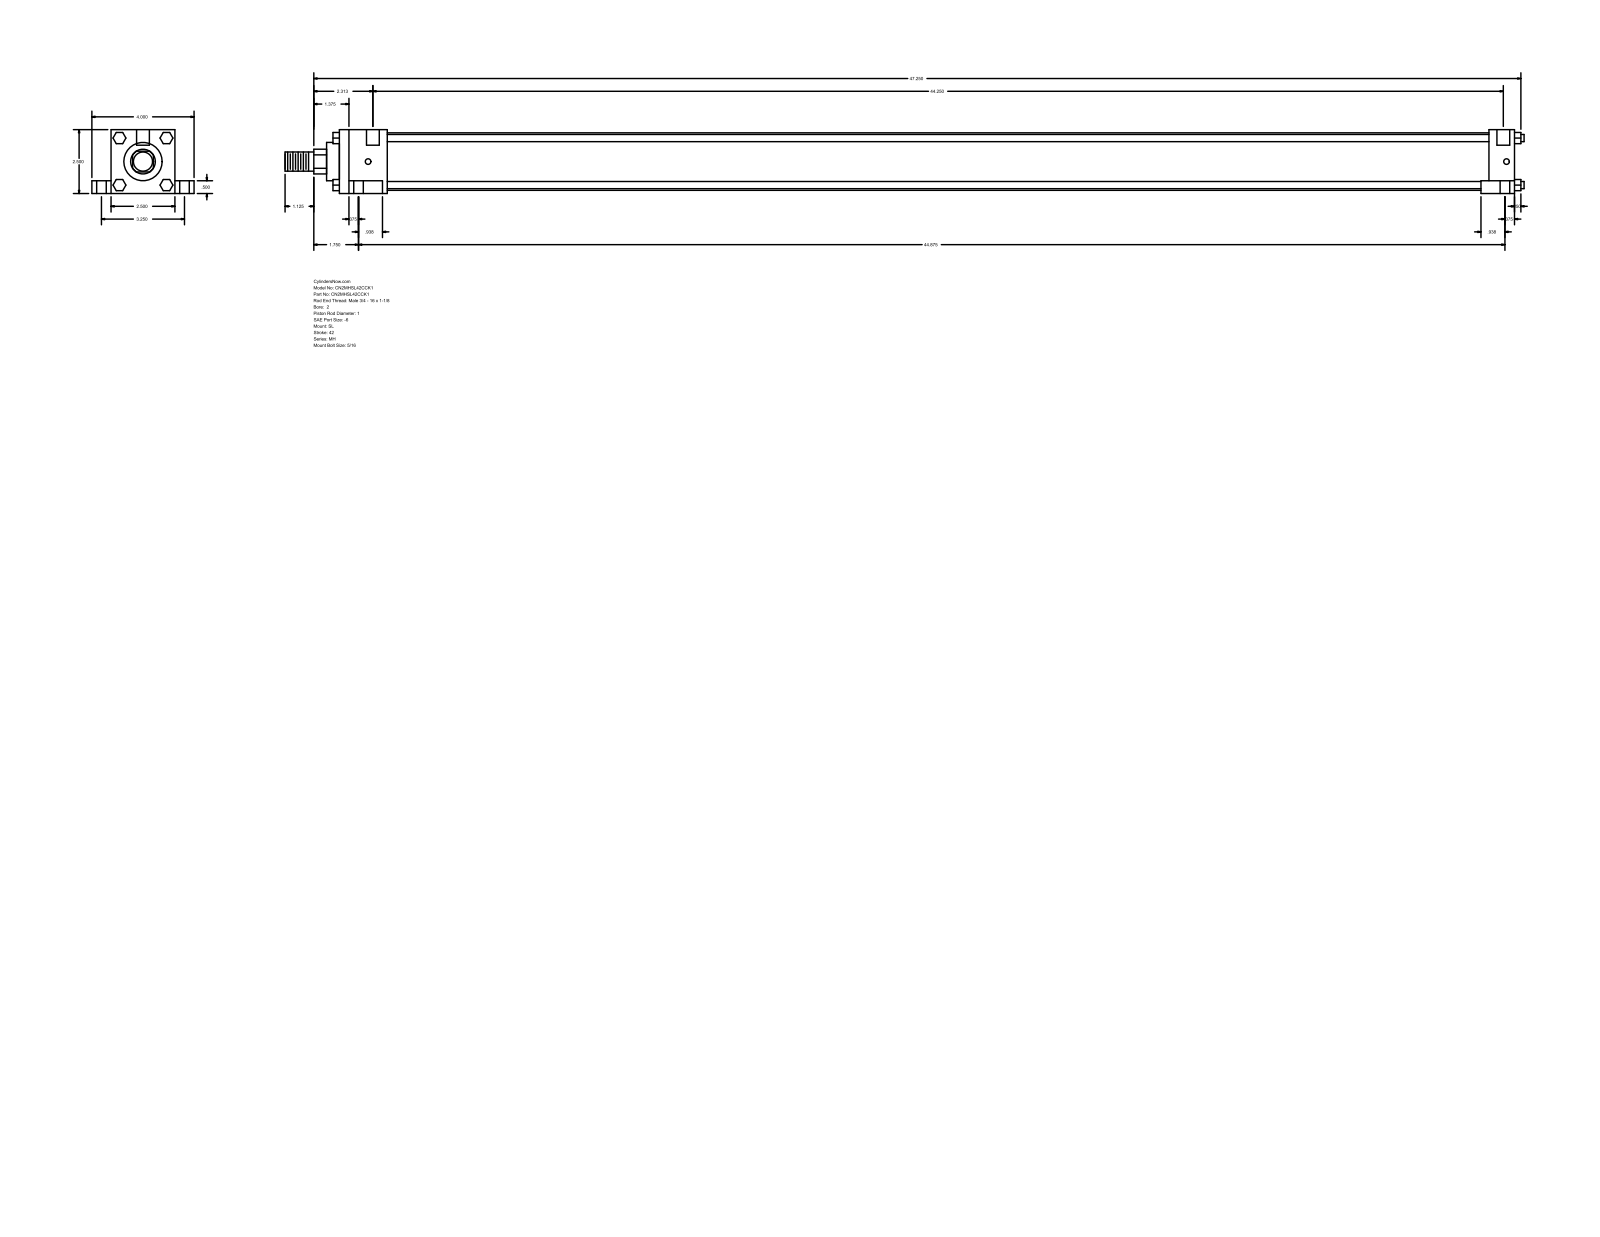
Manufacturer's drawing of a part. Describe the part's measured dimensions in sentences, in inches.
The part is named "MH_SL__0200_1". Its 3-D file was written by "GSSL Pune (CONFIG_CONTROL_DESIGN)". It is 0 solids with 148 faces: 112 planar, 36 cylindrical and 0 other. Overall it measures 48.5 by 4 by 2.5 inches. Round holes: 4 of diameter 0.219, 4 of diameter 0.375, 4 of diameter 0.625, 2 of diameter 0.5. Round bosses or shafts: 4 of diameter 0.281, 1 of diameter 2.25, 1 of diameter 1.5, 1 of diameter 1, 1 of diameter 0.75. Partial cylindrical surfaces (rounded edges, fillets, slot ends): 1 of radius 0.484. The main face-to-face distances are 2.5, 46, 0.5, 0.75, 2, 3.25, 1, 45, 1.875, 43.125. The hole center spacings are 1.626, 1.668, 1.719, 3.25, 44.343, 44.53, 44.562, 44.842.
